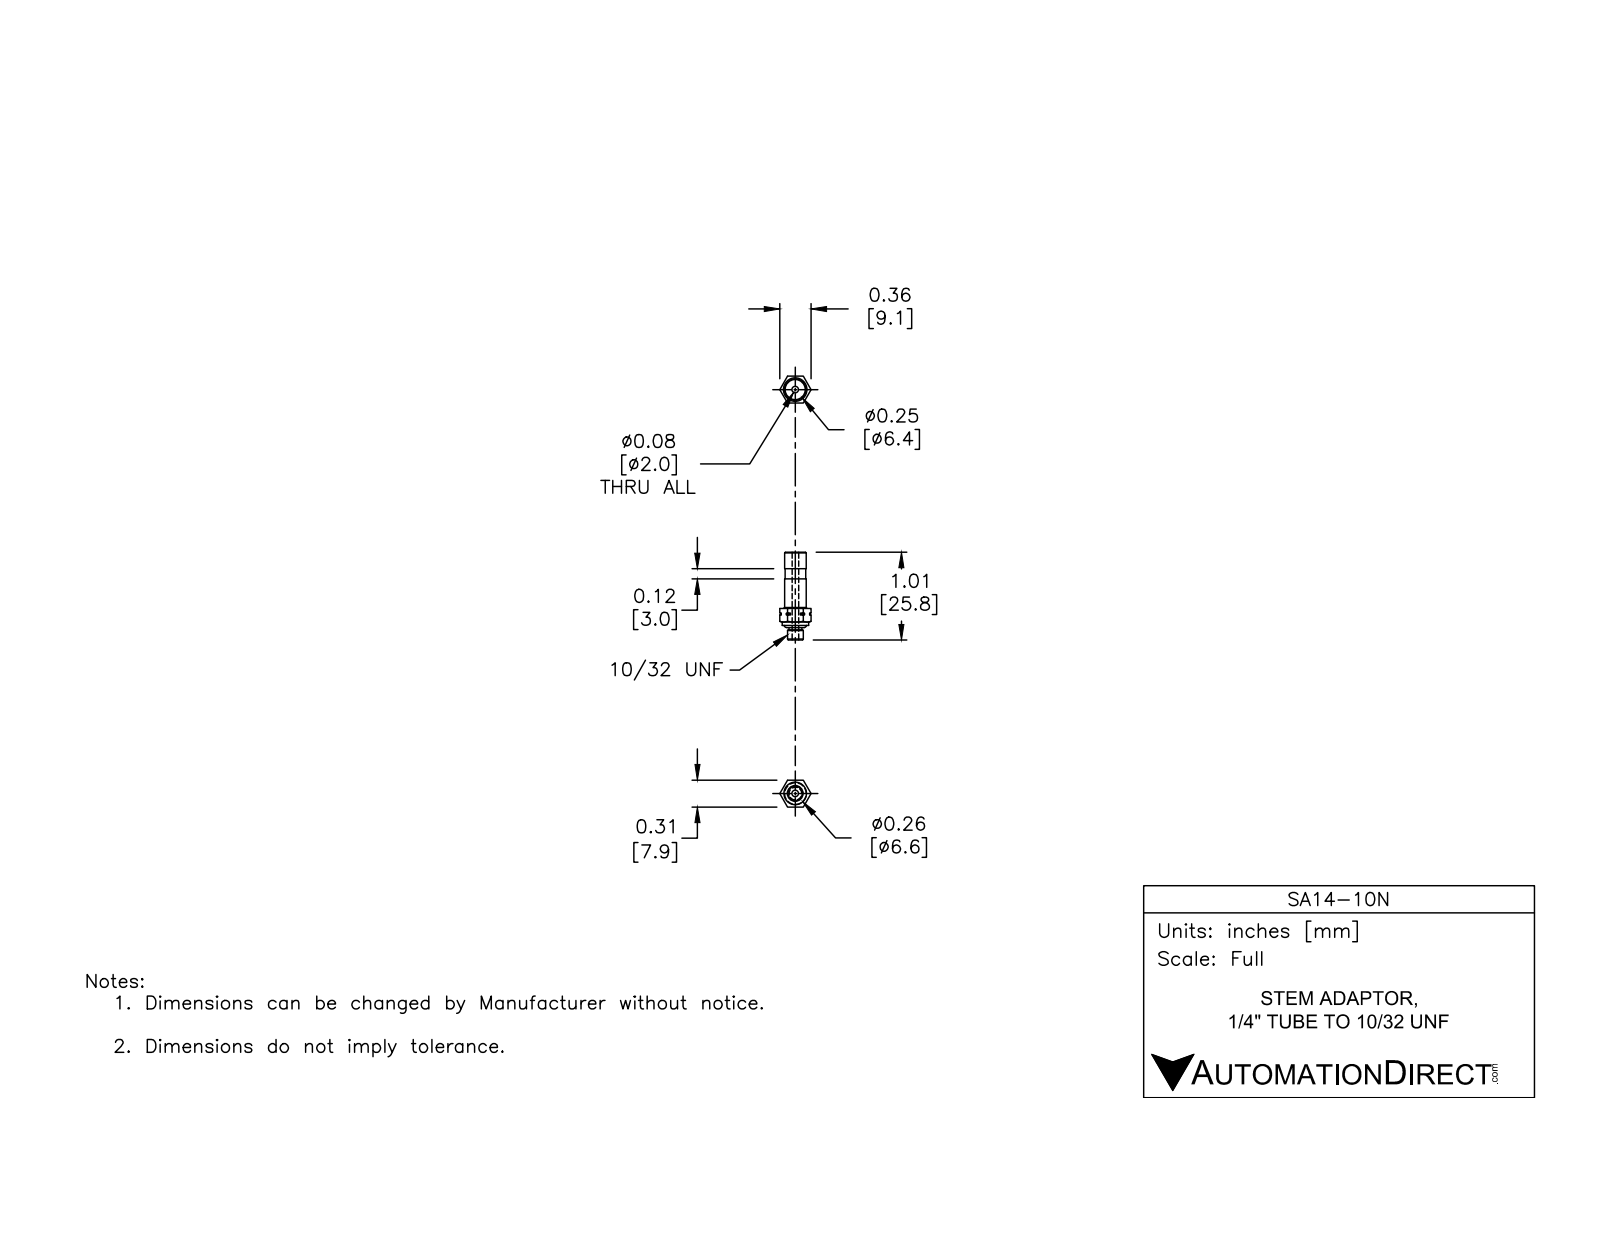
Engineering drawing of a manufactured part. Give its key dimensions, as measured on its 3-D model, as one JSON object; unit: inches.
{"part_name": "SA14-10N", "step_written_by": "SolidWorks 2015 (CONFIG_CONTROL_DESIGN)", "units": "inches", "bodies": {"solids": 2, "faces": 59, "planar": 13, "cylindrical": 20, "other": 26}, "overall_size": [1.014, 0.359, 0.311], "volume_in3": 0.048, "surface_area_in2": 1.32, "round_holes": [[0.077, 1]], "round_bosses_or_shafts": [[0.303, 1], [0.251, 1], [0.237, 1], [0.183, 1], [0.15, 1]], "partial_cylinders_radius": [[0.166, 1]], "face_to_face_distances": [0.311, 0.846, 0.197, 0.65, 0.167, 0.364, 1.014, 0.118, 0.705, 0.823]}
